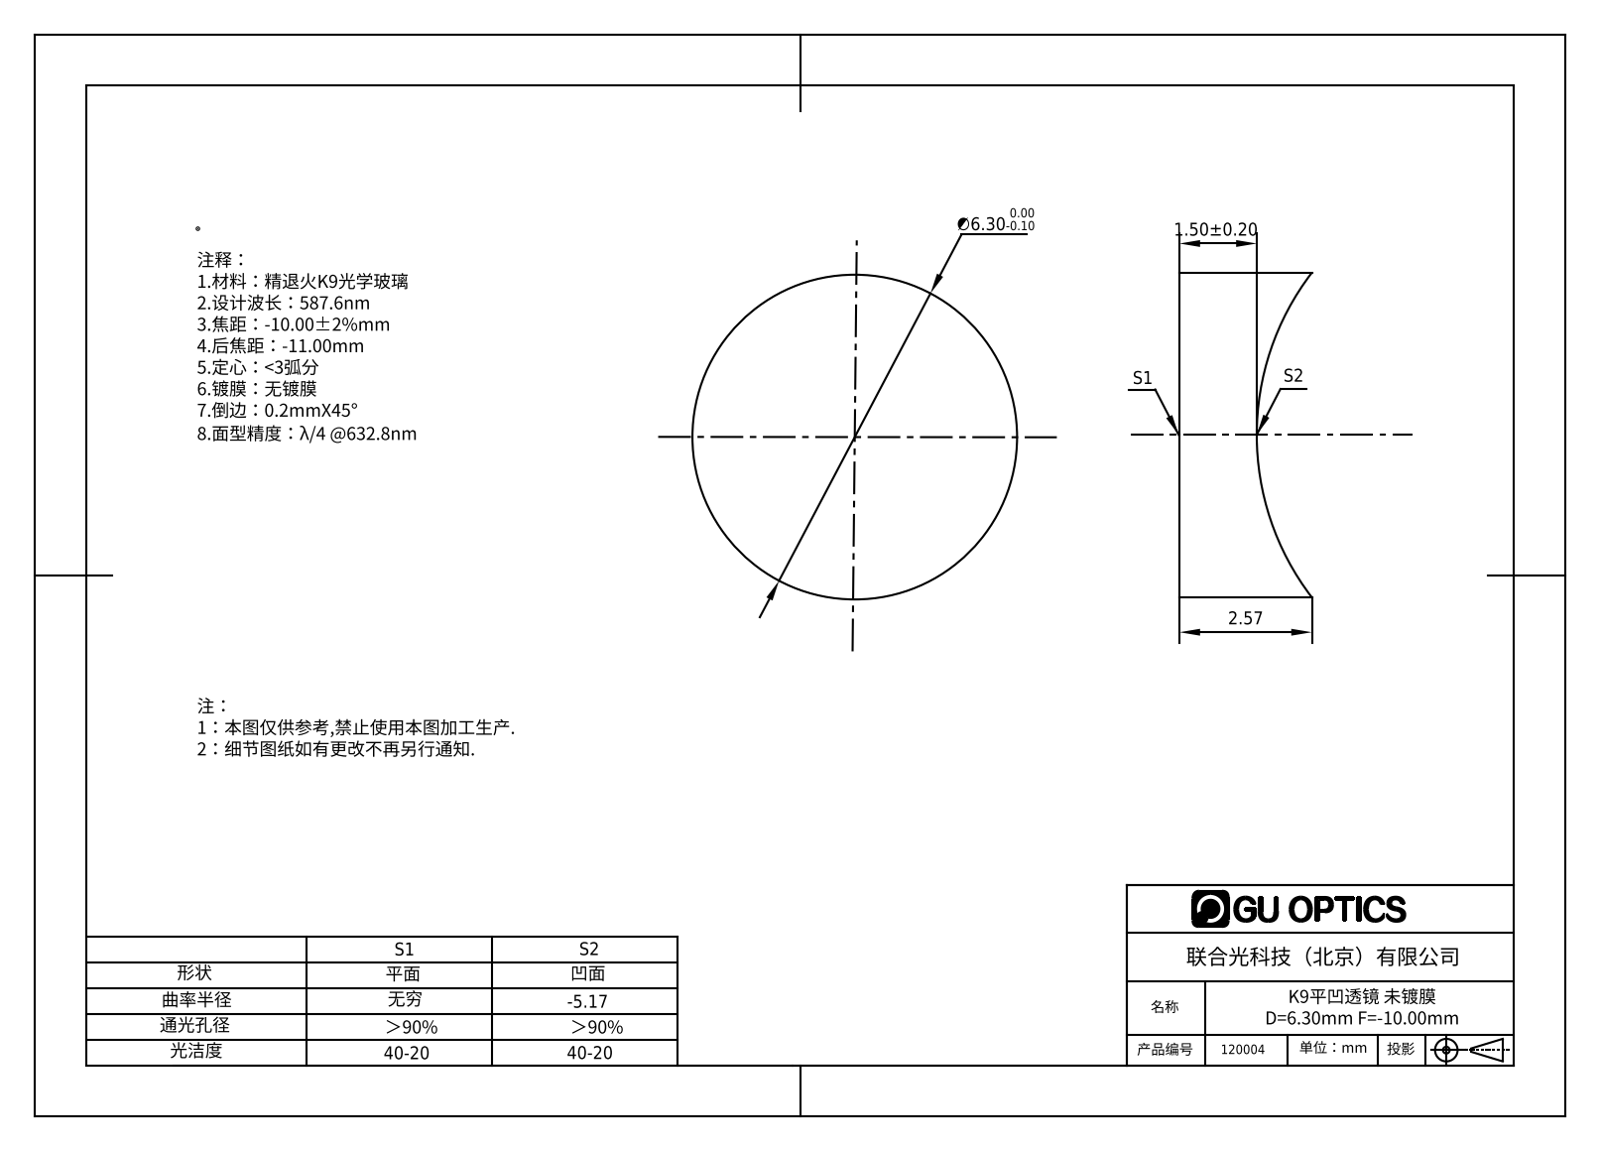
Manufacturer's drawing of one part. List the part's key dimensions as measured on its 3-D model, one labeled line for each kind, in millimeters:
Part name (STEP PRODUCT): 120004
STEP written by: SolidWorks 2016 (AUTOMOTIVE_DESIGN)
Units: millimetres
Bodies: 1 solid, 5 faces (1 planar, 2 cylindrical, 2 other)
Overall size (bounding box): 6.3 × 6.3 × 2.57
Volume: 63 mm³ · Surface area: 117 mm²
Round bosses / shafts (diameter × count): ⌀6.3 ×1
